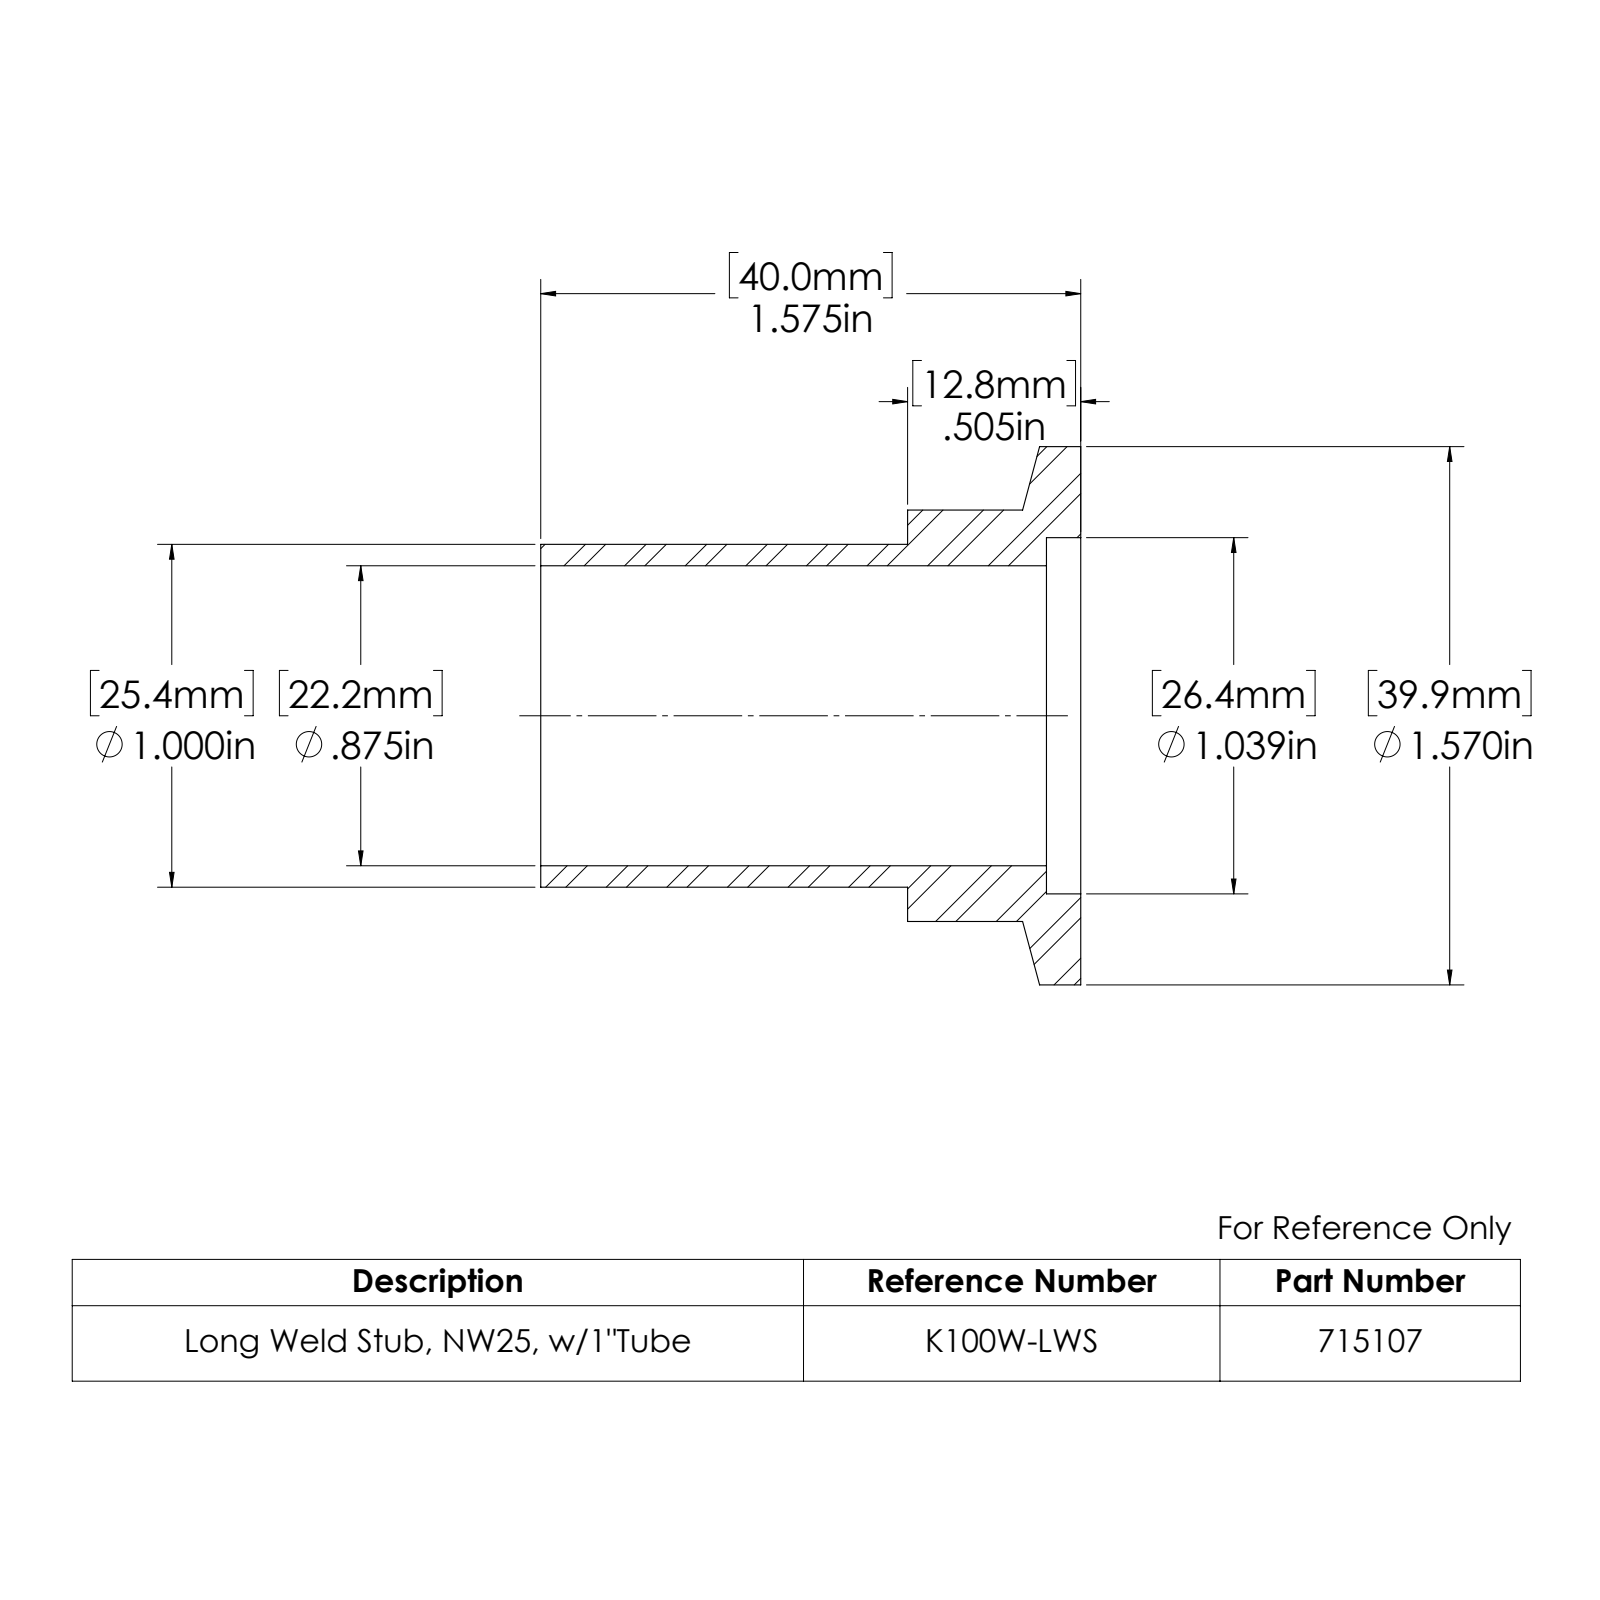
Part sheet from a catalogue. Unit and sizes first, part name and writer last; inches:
Units: inches
Overall size (bounding box): 1.575 × 1.57 × 1.57
Round holes (diameter × count): ⌀0.875 ×1, ⌀1.039 ×1
Round bosses / shafts (diameter × count): ⌀1.57 ×1, ⌀1.2 ×1, ⌀1 ×1
Main face-to-face distances: 0.505, 0.1, 0.405, 1.575, 1.475, 1.07
Volume: 0.555 in³ · Surface area: 12.3 in²
Bodies: 1 solid, 16 faces (4 planar, 10 cylindrical, 2 other)
Part name (STEP PRODUCT): 715107
STEP written by: SolidWorks 2022 (AUTOMOTIVE_DESIGN)
